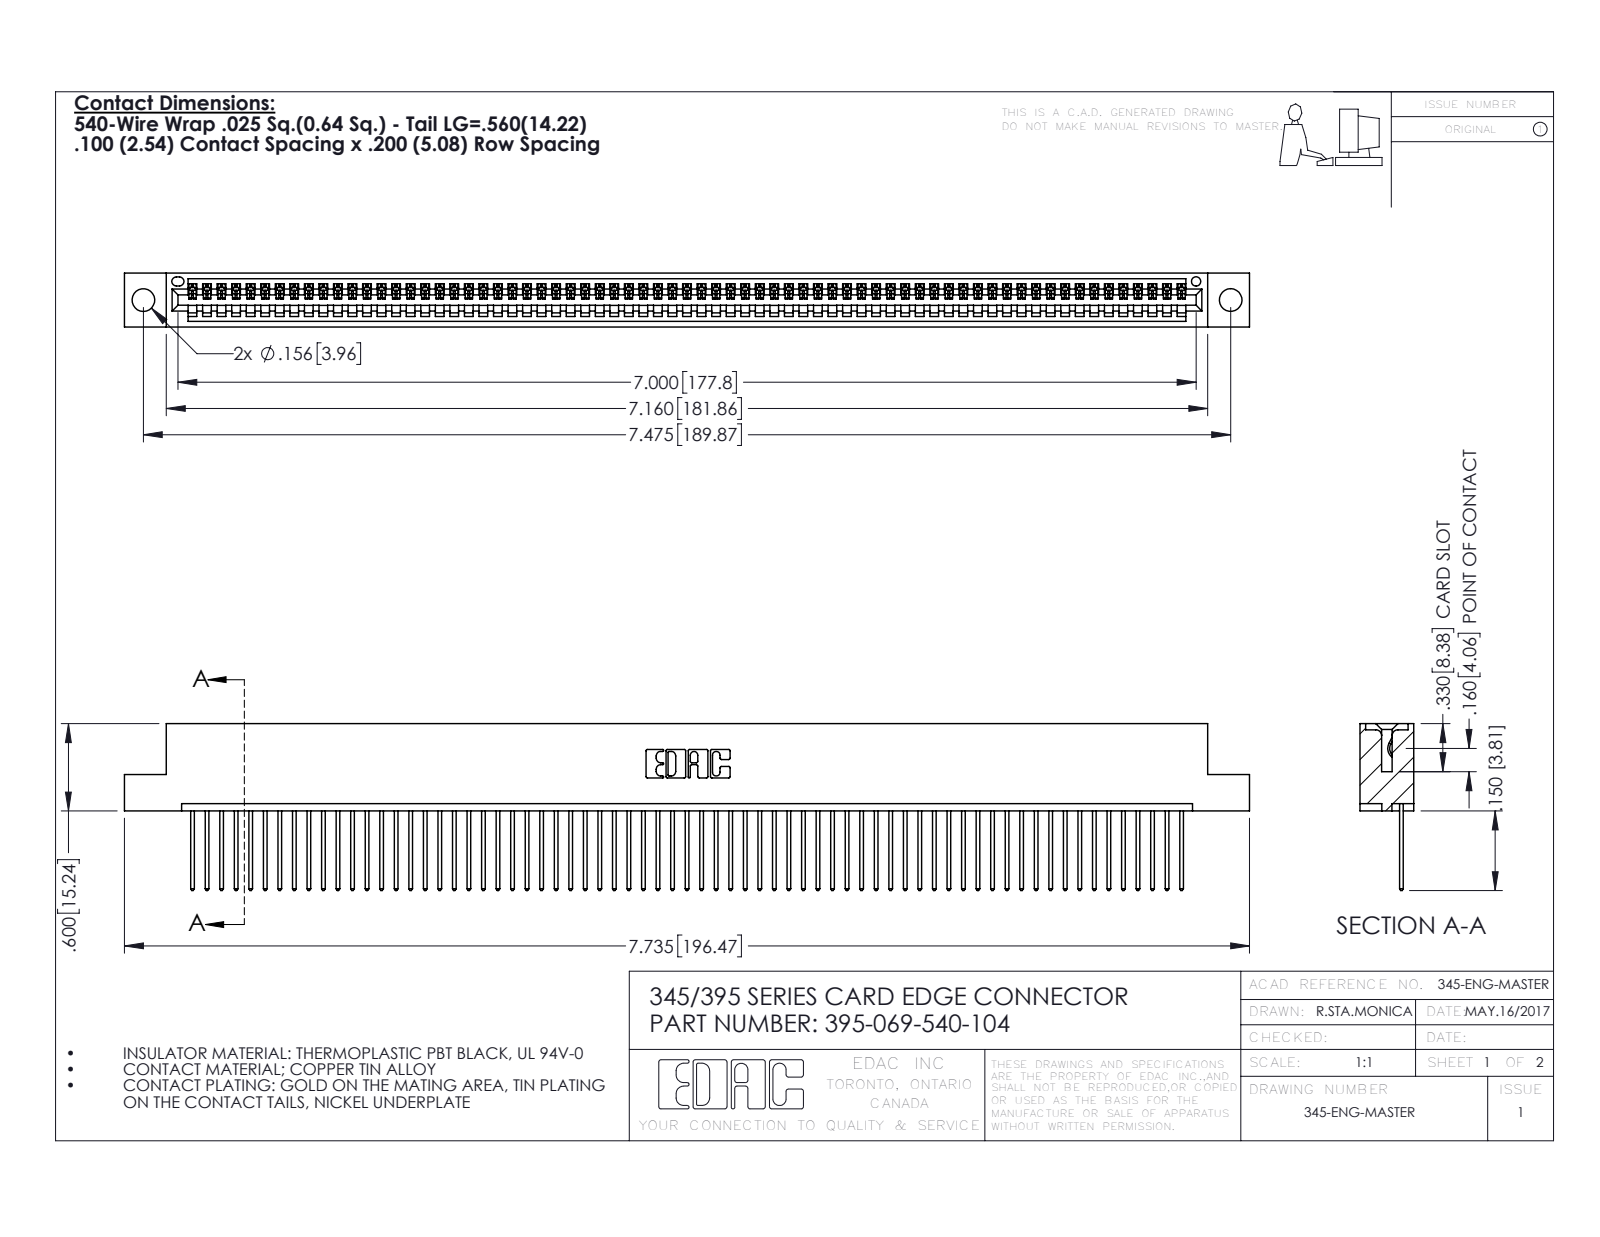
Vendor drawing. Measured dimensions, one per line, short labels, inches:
name: 395-069-540-104; 345 Part_Flush Mounting Lugs - 0.156 Dia-TH; 345-292-001_345-293-140
written by: SolidWorks 2016 (CONFIG_CONTROL_DESIGN)
unit: in
bodies: 70 solids, 4128 faces (2840 planar, 1288 cylindrical, 0 other)
size: 7.735 × 1.147 × 0.37
volume: 1.153 in³; area: 40.22 in²
holes: 2× ⌀0.156, 1× ⌀0.064
rounds: 138× R0.006, 138× R0.01, 22× R0.01, 6× R0.007, 6× R0.031, 3× R0.026, 2× R0.031, 2× R0.04
face distances: 0.072, 0.298, 0.37, 0.098, 0.272, 0.025, 0.2, 0.225, 0.149, 0.072
hole spacings: 0.27, 7.239, 7.475
